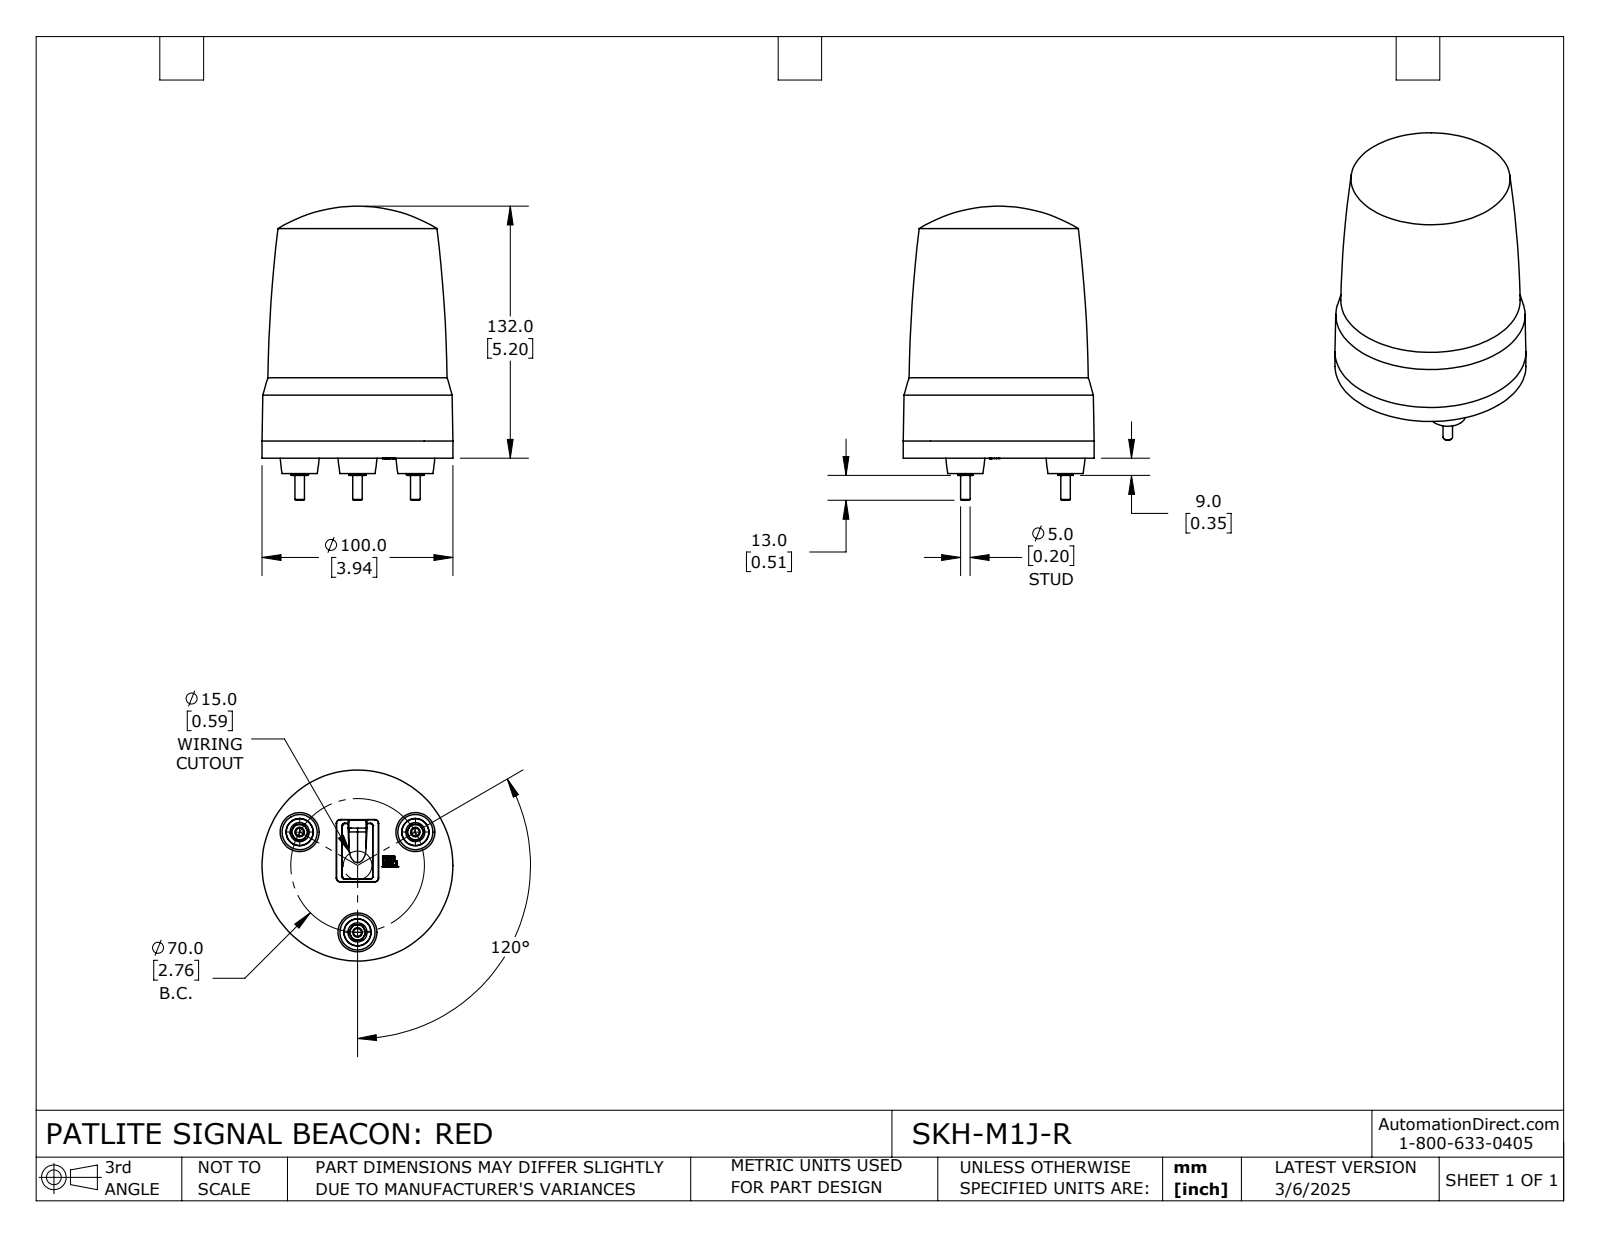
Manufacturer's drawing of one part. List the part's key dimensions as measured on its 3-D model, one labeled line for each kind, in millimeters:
Part name (STEP PRODUCT): SKH-M1J-R
STEP written by: SolidWorks 2024 (CONFIG_CONTROL_DESIGN)
Units: millimetres
Bodies: 1 solid, 327 faces (159 planar, 14 cylindrical, 154 other)
Overall size (bounding box): 154 × 100 × 100
Volume: 859 960 mm³ · Surface area: 52 586 mm²
Round bosses / shafts (diameter × count): ⌀10 ×3, ⌀5 ×3, ⌀100 ×1
Main face-to-face distances: 8, 0.85, 8.85, 1.6, 10.45, 2.45, 3.8, 4.2, 5.05, 6.65
